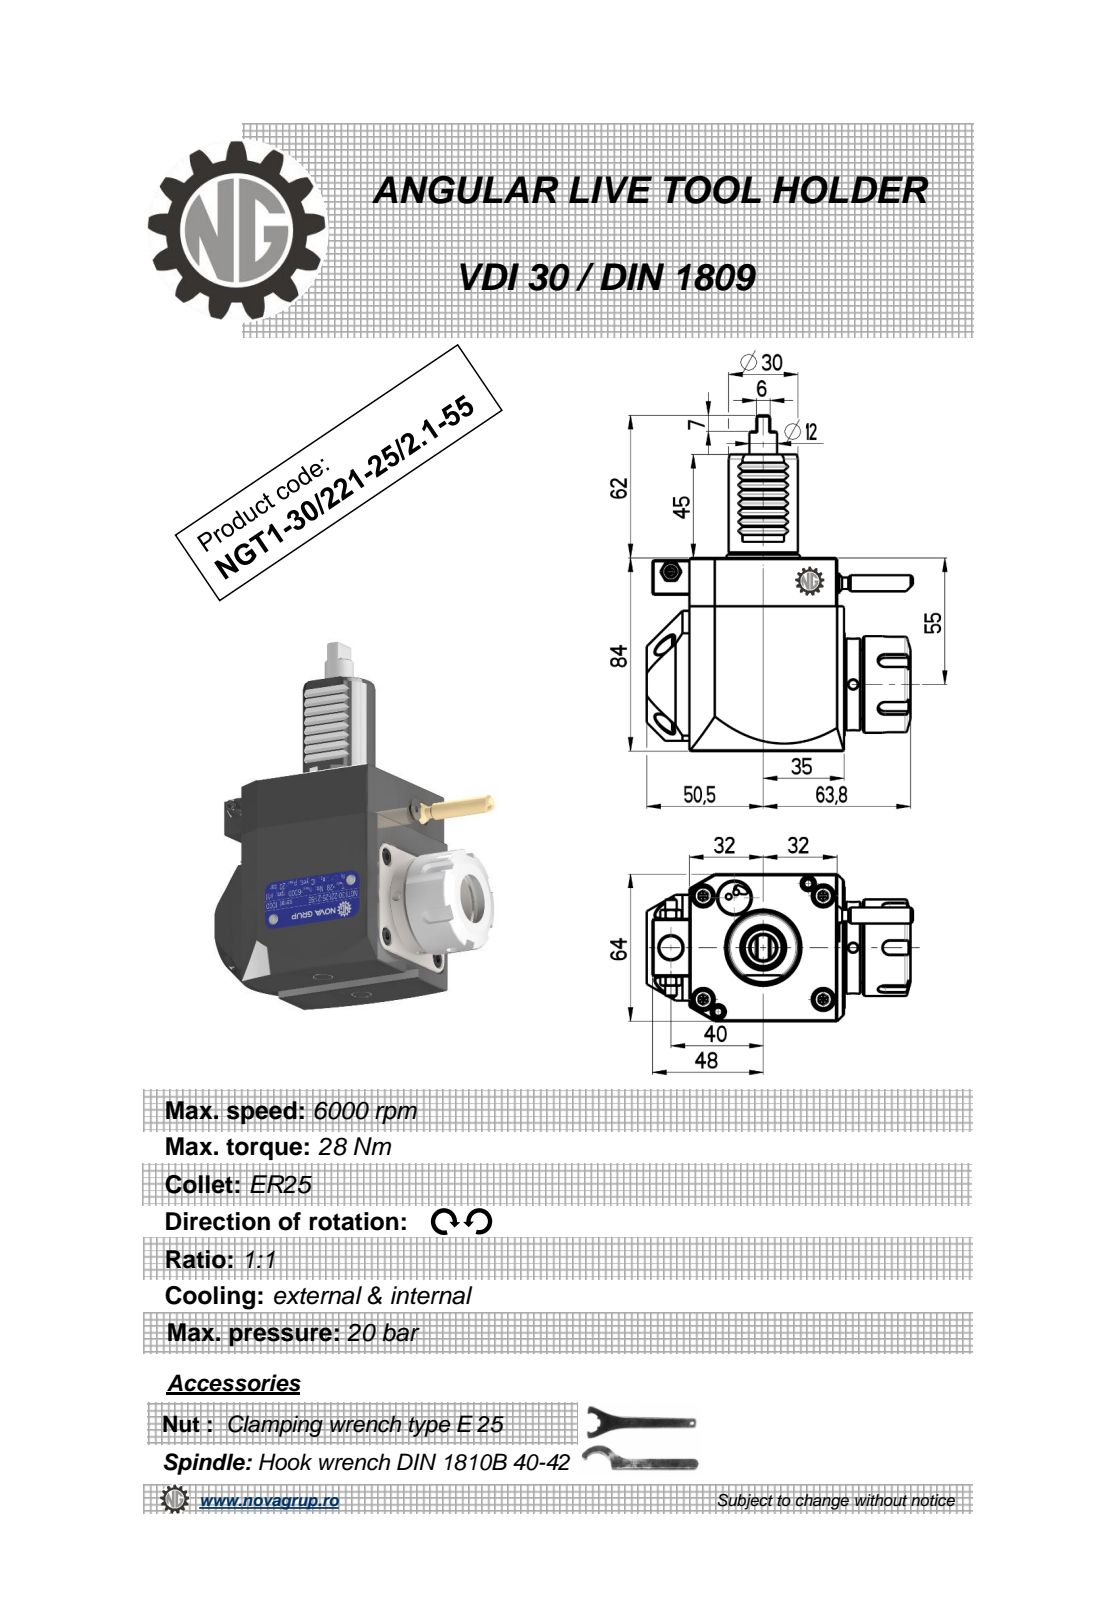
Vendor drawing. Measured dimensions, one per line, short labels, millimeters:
name: NGT1_30_221_25_2_1_55
written by: PRO/ENGINEER BY PARAMETRIC TECHNOLOGY CORPORATION, 2010280 (CONFIG_CONTROL_DESIGN)
unit: mm
bodies: 1 solid, 404 faces (181 planar, 84 cylindrical, 139 other)
size: 146 × 115.38 × 65.6
volume: 451 657 mm³; area: 45 717 mm²
holes: 2× ⌀4, 1× ⌀2.5, 1× ⌀3, 1× ⌀4.2, 1× ⌀9.5, 1× ⌀10, 1× ⌀20.3
bosses: 2× ⌀8.96, 2× ⌀5, 1× ⌀42, 1× ⌀40, 1× ⌀33, 1× ⌀30, 1× ⌀12, 1× ⌀7
rounds: 12× R0.26, 8× R0.3, 5× R3, 2× R0.8, 2× R160, 1× R32
face distances: 64, 84, 67.2, 3.2, 67, 3, 80, 0.5, 18.5, 82.5
hole spacings: 14.22, 46.17, 46.5, 78.95, 92.92
